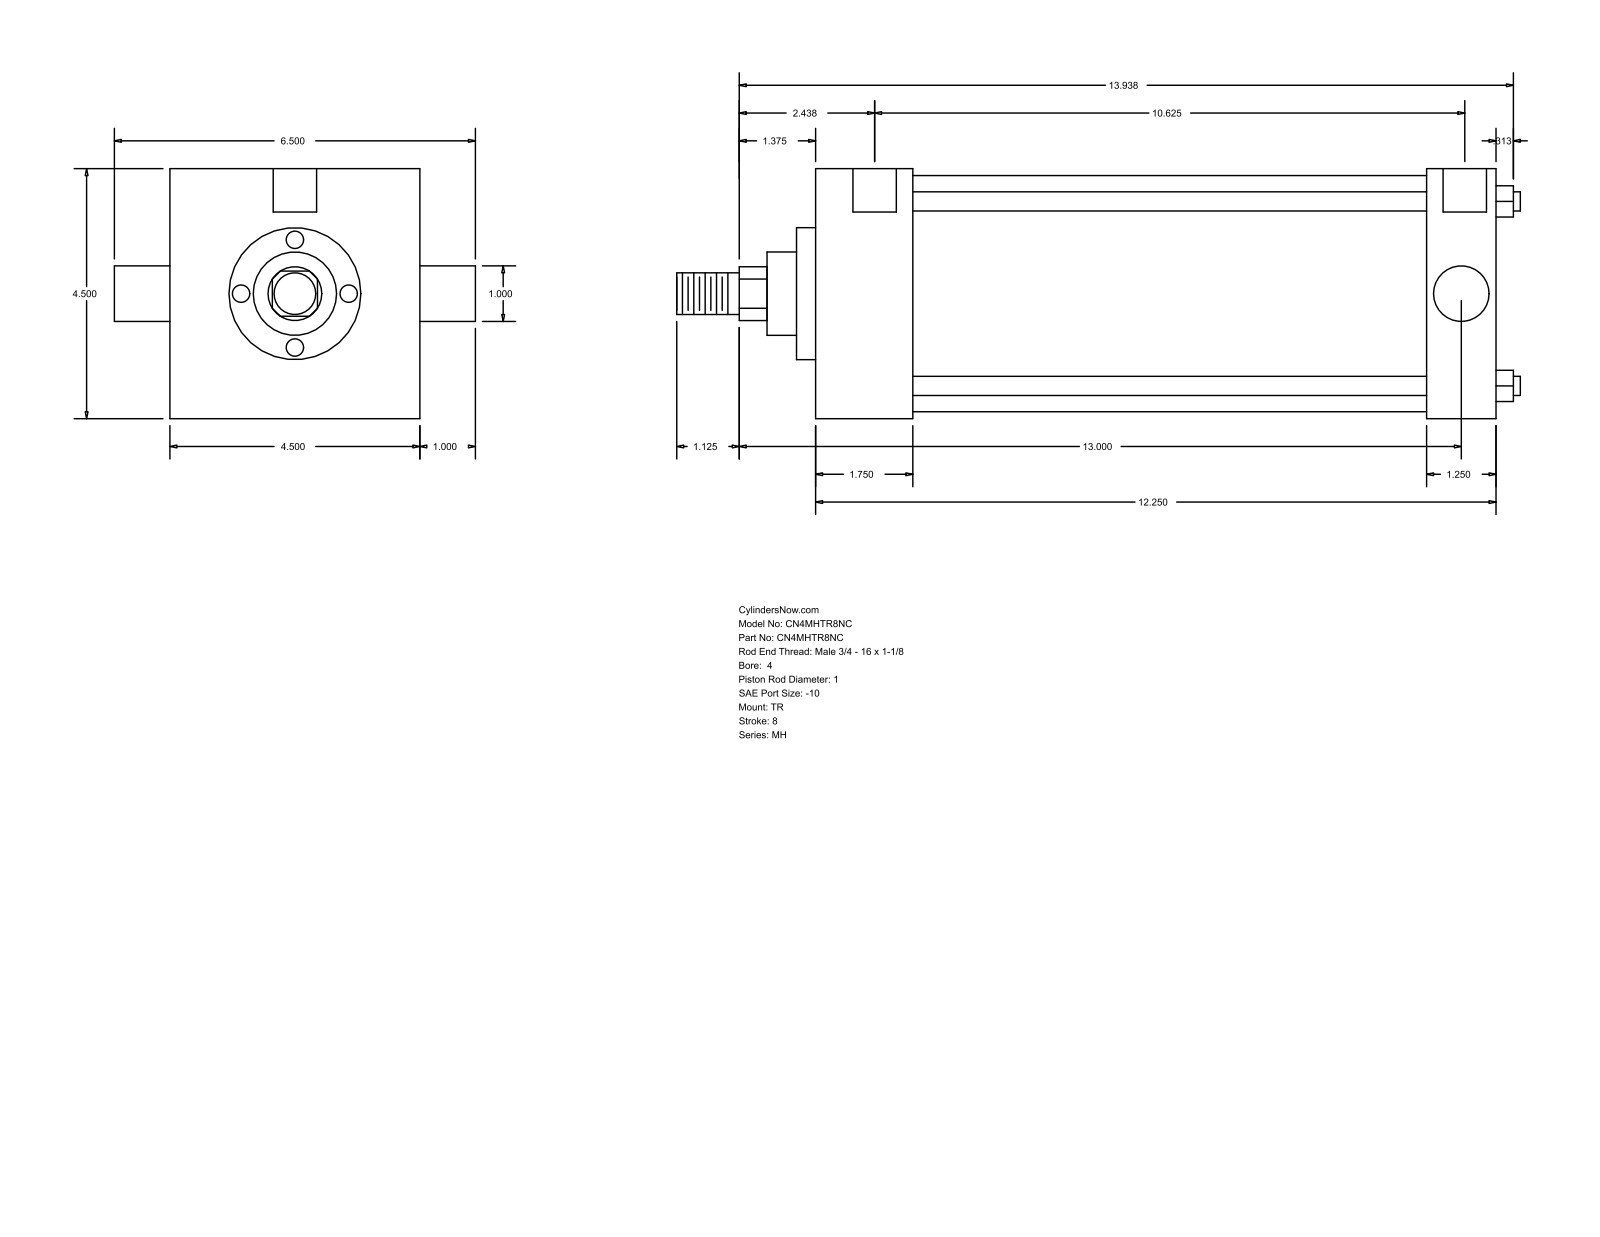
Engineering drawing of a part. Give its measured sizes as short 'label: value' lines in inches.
name: MH_TR__0400_1
written by: GSSL Pune (CONFIG_CONTROL_DESIGN)
unit: in
bodies: 0 solids, 86 faces (61 planar, 25 cylindrical, 0 other)
size: 15.187 × 6.5 × 4.5
holes: 3× ⌀0.344, 2× ⌀0.781
bosses: 4× ⌀0.345, 2× ⌀1, 1× ⌀4.25, 1× ⌀2.375, 1× ⌀1.5, 1× ⌀0.75
rounds: 1× R0.484
face distances: 4.5, 12.25, 1.75, 10.5, 11, 9.25, 1.25, 0.344, 2.094, 11.344
hole spacings: 0.062, 0.063, 10.625, 10.687, 10.688, 10.75
